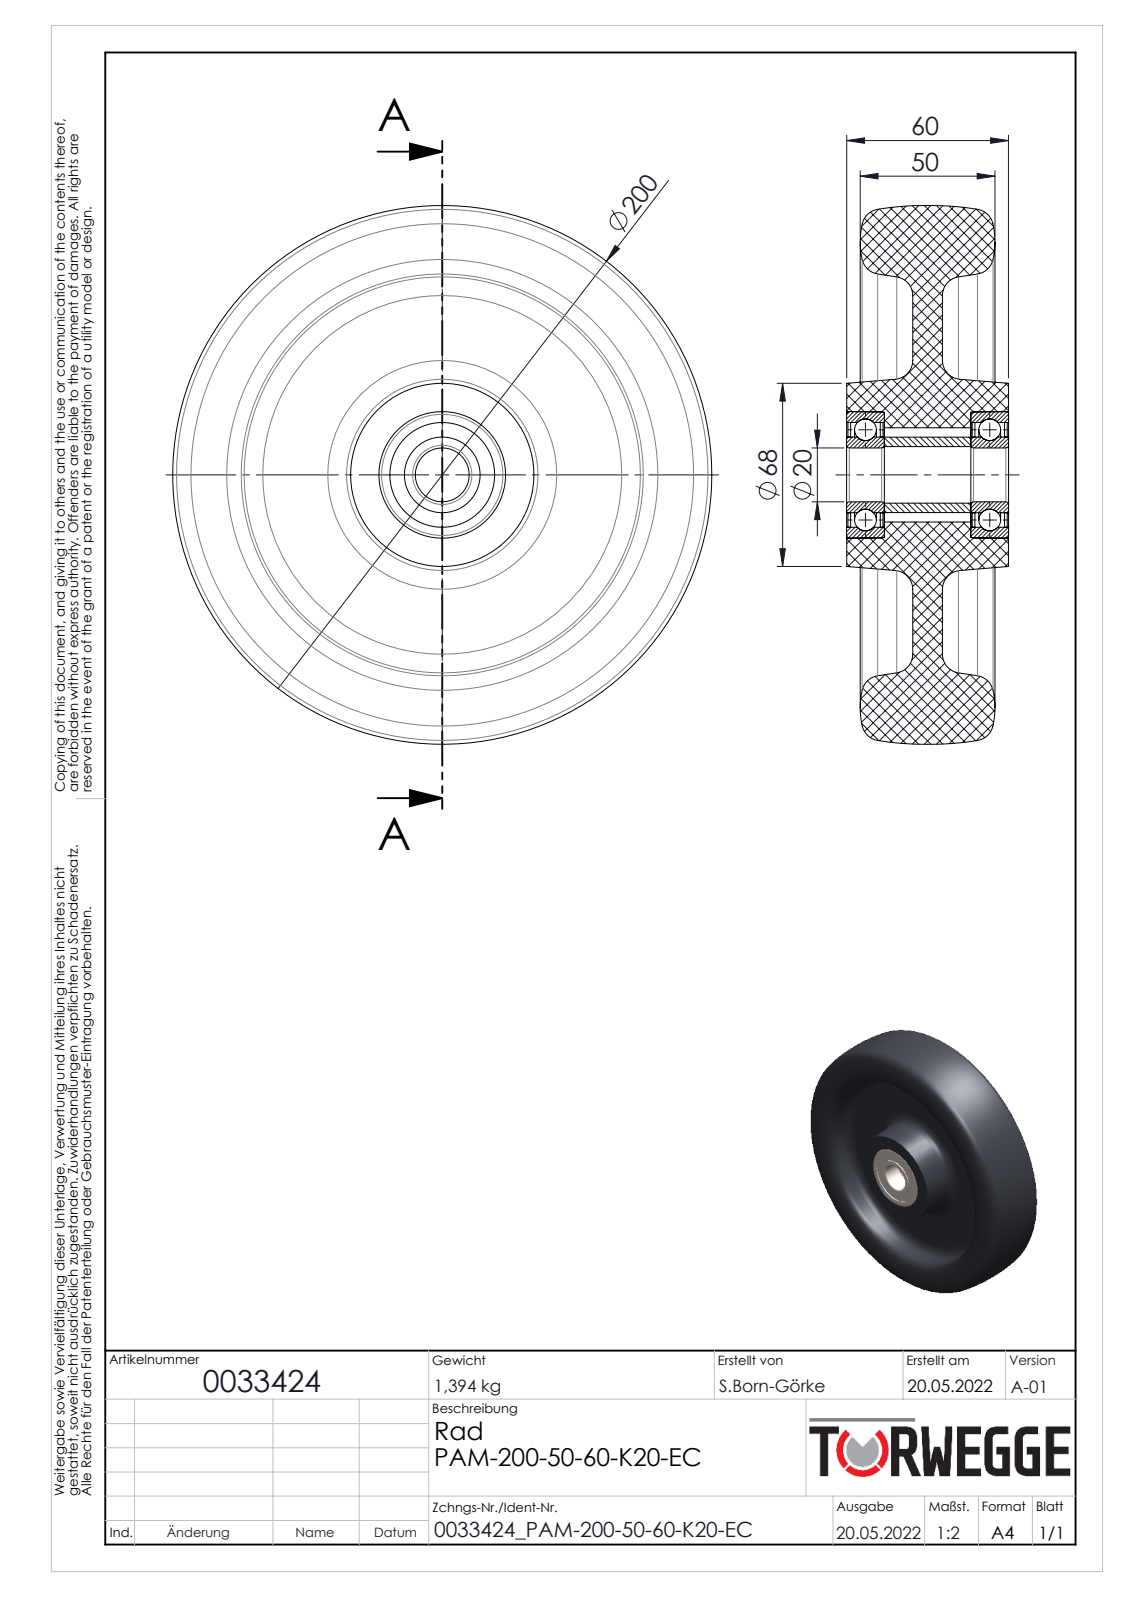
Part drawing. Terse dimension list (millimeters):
name: 0033424
written by: SolidWorks 2020 (AUTOMOTIVE_DESIGN)
unit: mm
bodies: 12 solids, 142 faces (24 planar, 46 cylindrical, 72 other)
size: 200.02 × 200 × 60.1
volume: 1 012 000 mm³; area: 145 159 mm²
holes: 1× ⌀20, 1× ⌀21, 1× ⌀28.1, 1× ⌀35, 1× ⌀38.9
bosses: 1× ⌀47, 1× ⌀28
face distances: 11, 24.5, 35.5, 46.1, 46.05, 14, 0.5, 1.5, 12.5, 13.5
